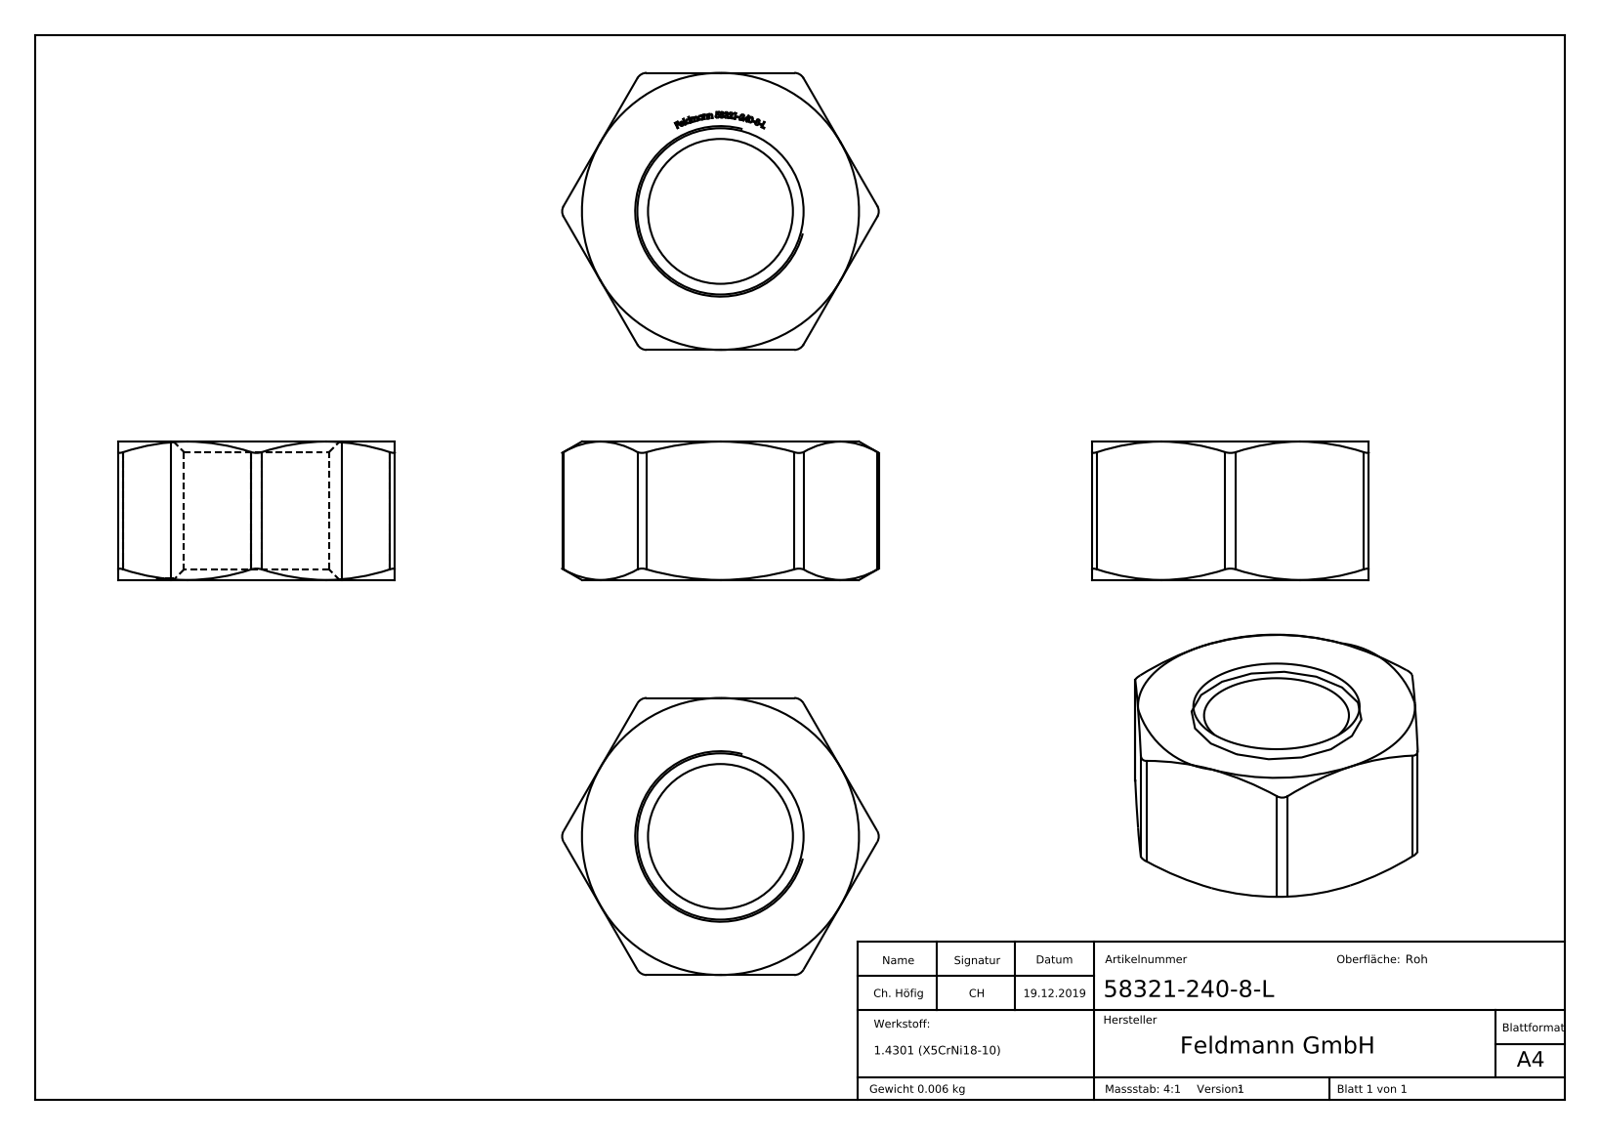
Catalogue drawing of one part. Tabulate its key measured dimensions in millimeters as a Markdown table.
| quantity | value |
| --- | --- |
| part name | 58321-240-8-L |
| STEP written by | SolidWorks 2015 (CONFIG_CONTROL_DESIGN) |
| units | millimeters |
| bodies | 1 solid, 29 faces (8 planar, 7 cylindrical, 14 other) |
| overall size | 22 × 14.86 × 13 |
| volume | 704 mm³ |
| surface area | 624 mm² |
| round holes (diameter × count) | 6.8 × 1 |
| partial cylindrical surfaces (radius × count) | 0.5 × 6 |
| main face-to-face distances | 13, 6.5 |
